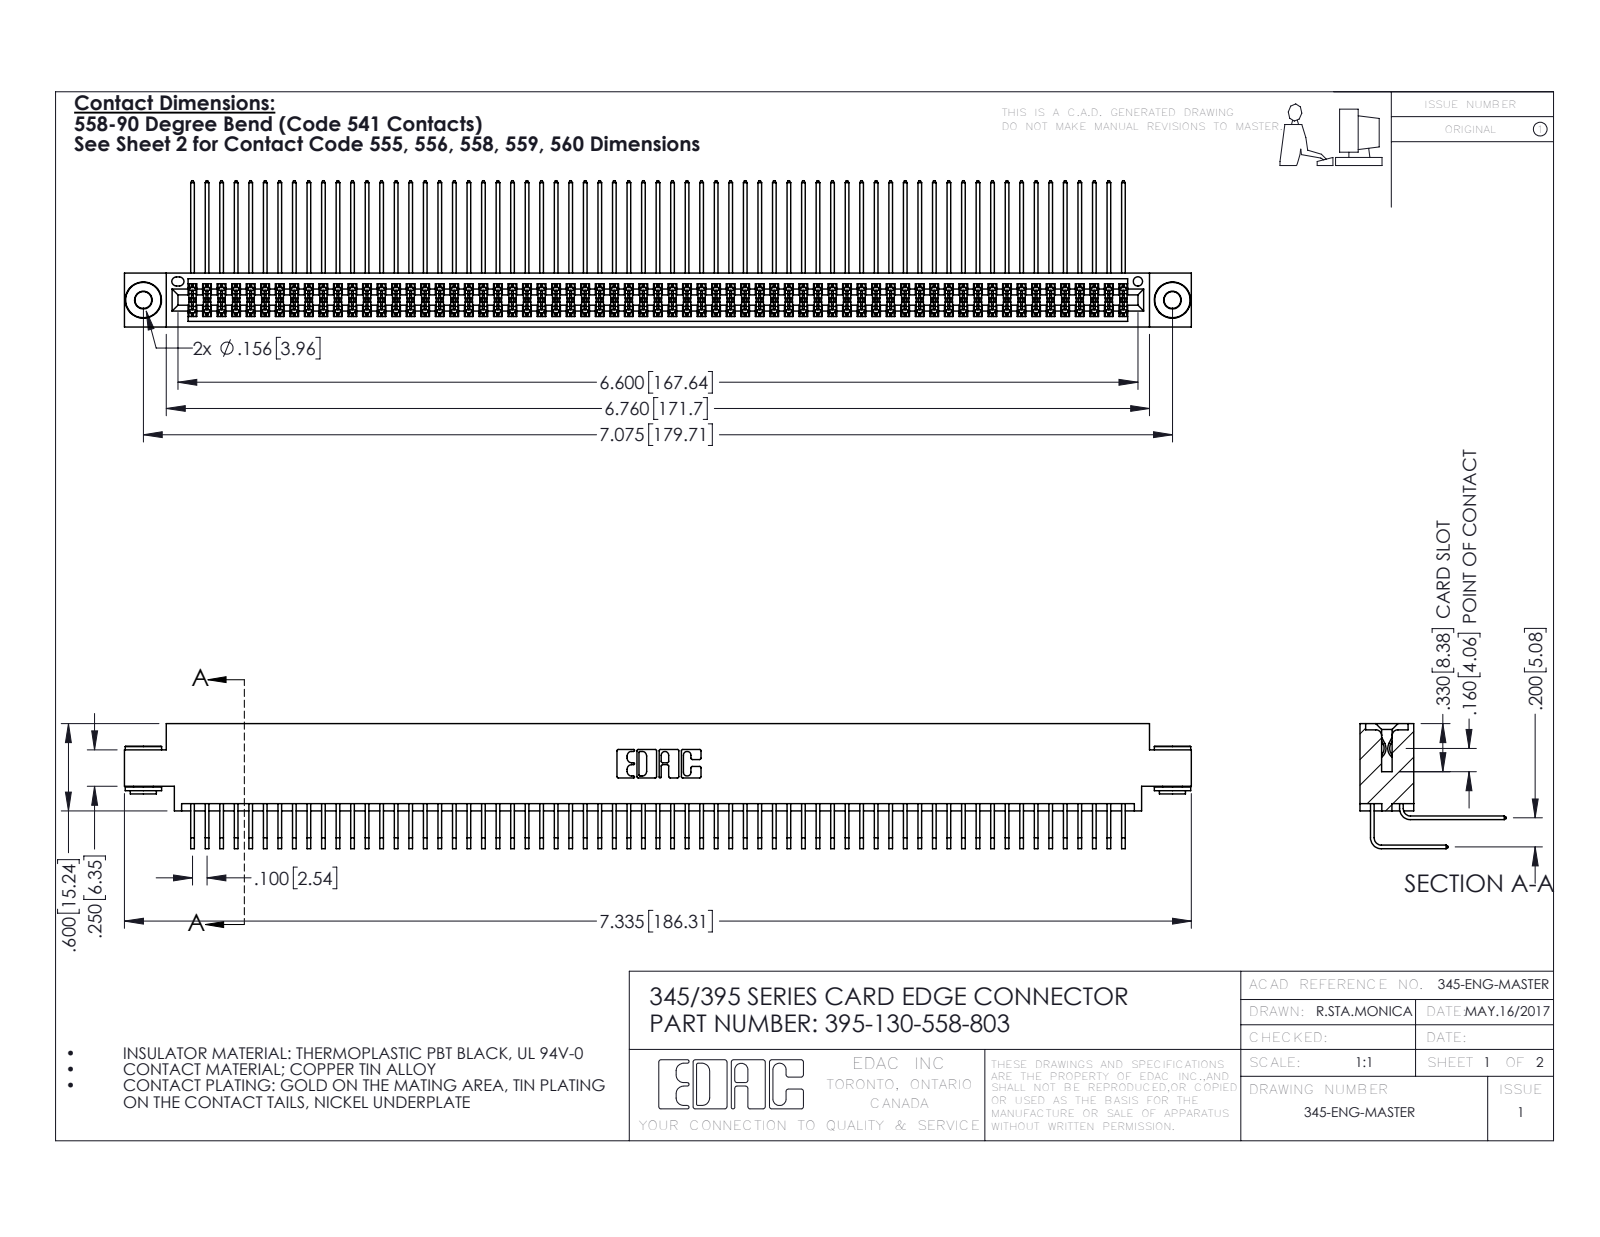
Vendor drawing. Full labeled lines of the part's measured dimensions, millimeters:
Part name (STEP PRODUCT): 395-130-558-803; 345-292-001_558 559 Tail - 1; 345-250-002_345-250-002-102; 345-292-001_558 Tail - 2 (+1 more)
STEP written by: SolidWorks 2016 (CONFIG_CONTROL_DESIGN)
Units: millimetres
Bodies: 133 solids, 6928 faces (4644 planar, 2276 cylindrical, 8 other)
Overall size (bounding box): 186.3 × 25.5 × 21.8
Volume: 18 960 mm³ · Surface area: 32 350 mm²
Round holes (diameter × count): ⌀2.9 ×2, ⌀4 ×2, ⌀1.6 ×1
Round bosses / shafts (diameter × count): ⌀6.4 ×2, ⌀4.6 ×2, ⌀3.5 ×2
Partial cylindrical surfaces — rounded edges, fillets, slot ends (radius × count): R0.2 ×196, R0.3 ×22, R0.2 ×6, R0.8 ×6, R0.7 ×3, R0.4 ×2, R0.5 ×2, R0.6 ×2
Main face-to-face distances: 1.8, 7.6, 5.1, 9.4, 2.5, 6.9, 0.6, 5.7, 4.4, 0.6
Hole centre spacings: 6.9, 173.7, 179.7
